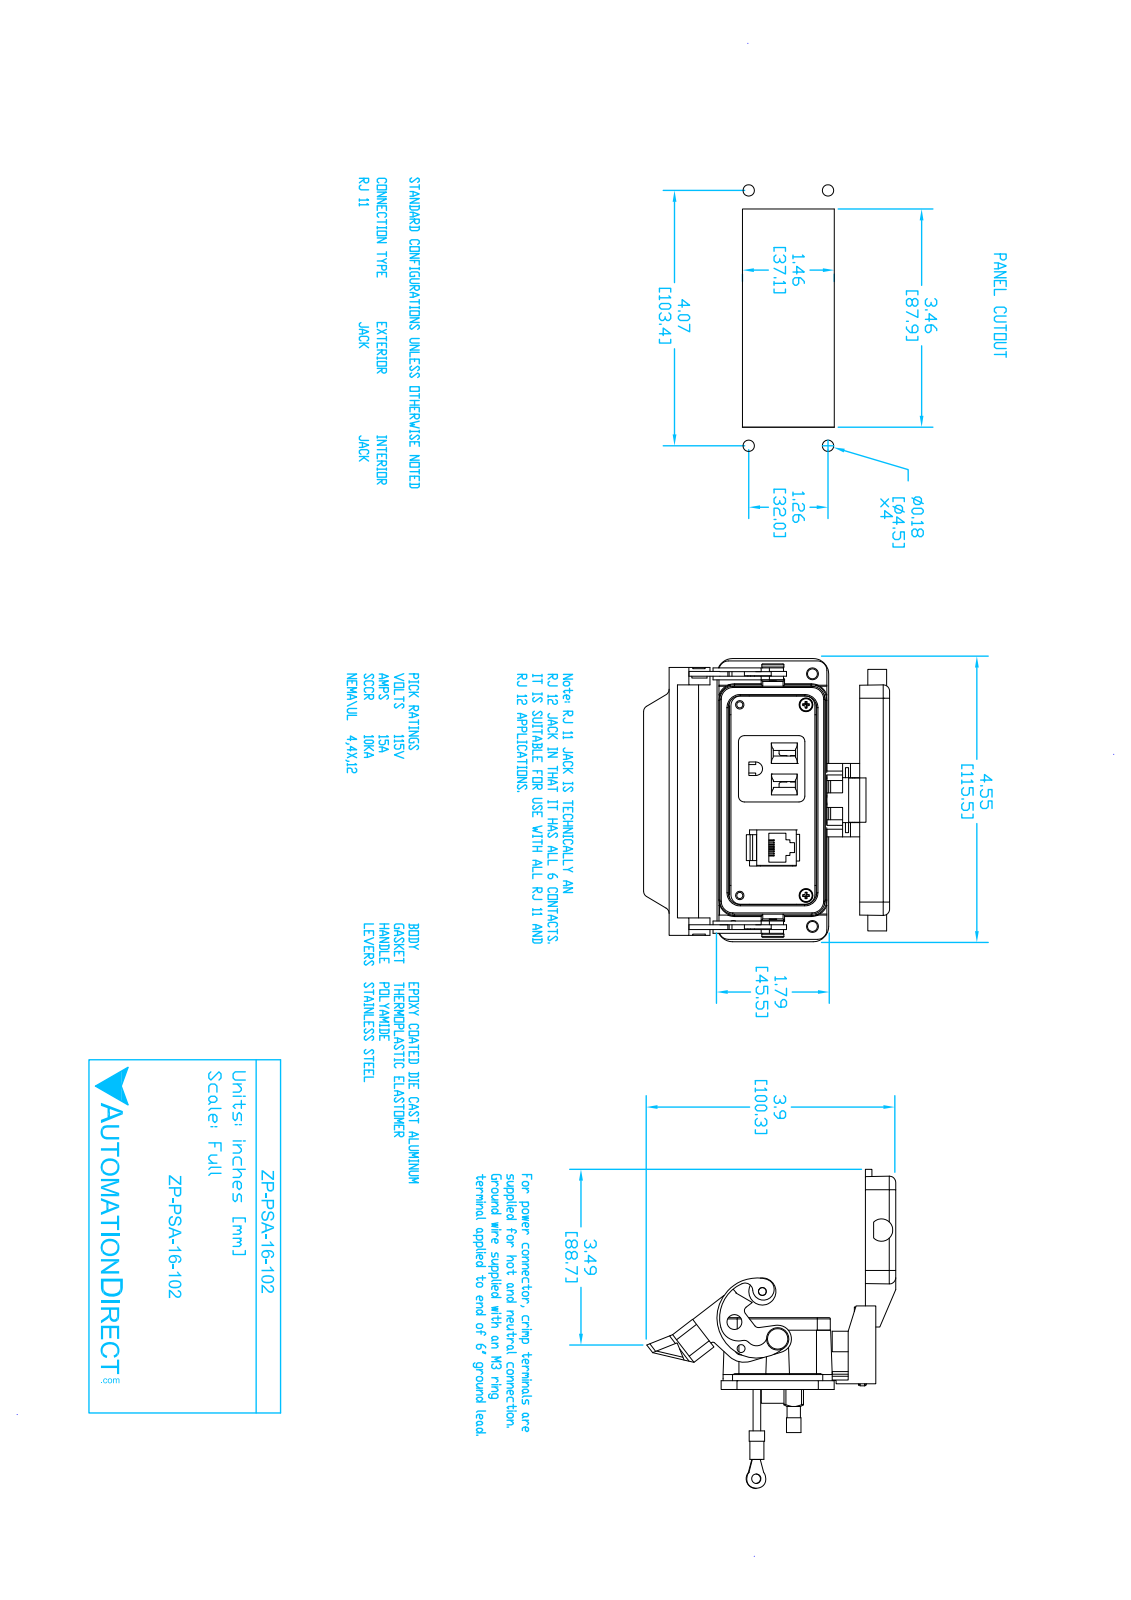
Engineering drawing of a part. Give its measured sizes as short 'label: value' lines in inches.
name: ZP-PSA-16-102
written by: SolidWorks 2017 (AUTOMOTIVE_DESIGN)
unit: in
bodies: 1 solid, 1451 faces (902 planar, 369 cylindrical, 180 other)
size: 5.064 × 4.547 × 3.968
volume: 6.177 in³; area: 105.1 in²
holes: 6× ⌀0.16, 4× ⌀0.098, 4× ⌀0.144, 4× ⌀0.19, 2× ⌀0.12, 2× ⌀0.15, 1× ⌀0.075, 1× ⌀0.085, 1× ⌀0.125, 1× ⌀0.13, 1× ⌀0.157, 1× ⌀0.163
bosses: 4× ⌀0.226, 4× ⌀0.22, 4× ⌀0.118, 2× ⌀0.23, 2× ⌀0.21, 2× ⌀0.1, 1× ⌀0.43, 1× ⌀0.354
rounds: 16× R0.1, 13× R0.15, 12× R0.031, 10× R0.02, 9× R0.015, 8× R0.025, 8× R0.094, 8× R0.25
face distances: 0.06, 0.672, 0.732, 0.135, 0.115, 0.02, 0.48, 4.067, 1.543, 1.604
hole spacings: 0.502, 1.261, 3.564, 3.748, 1.063, 1.26, 3.071, 3.25
